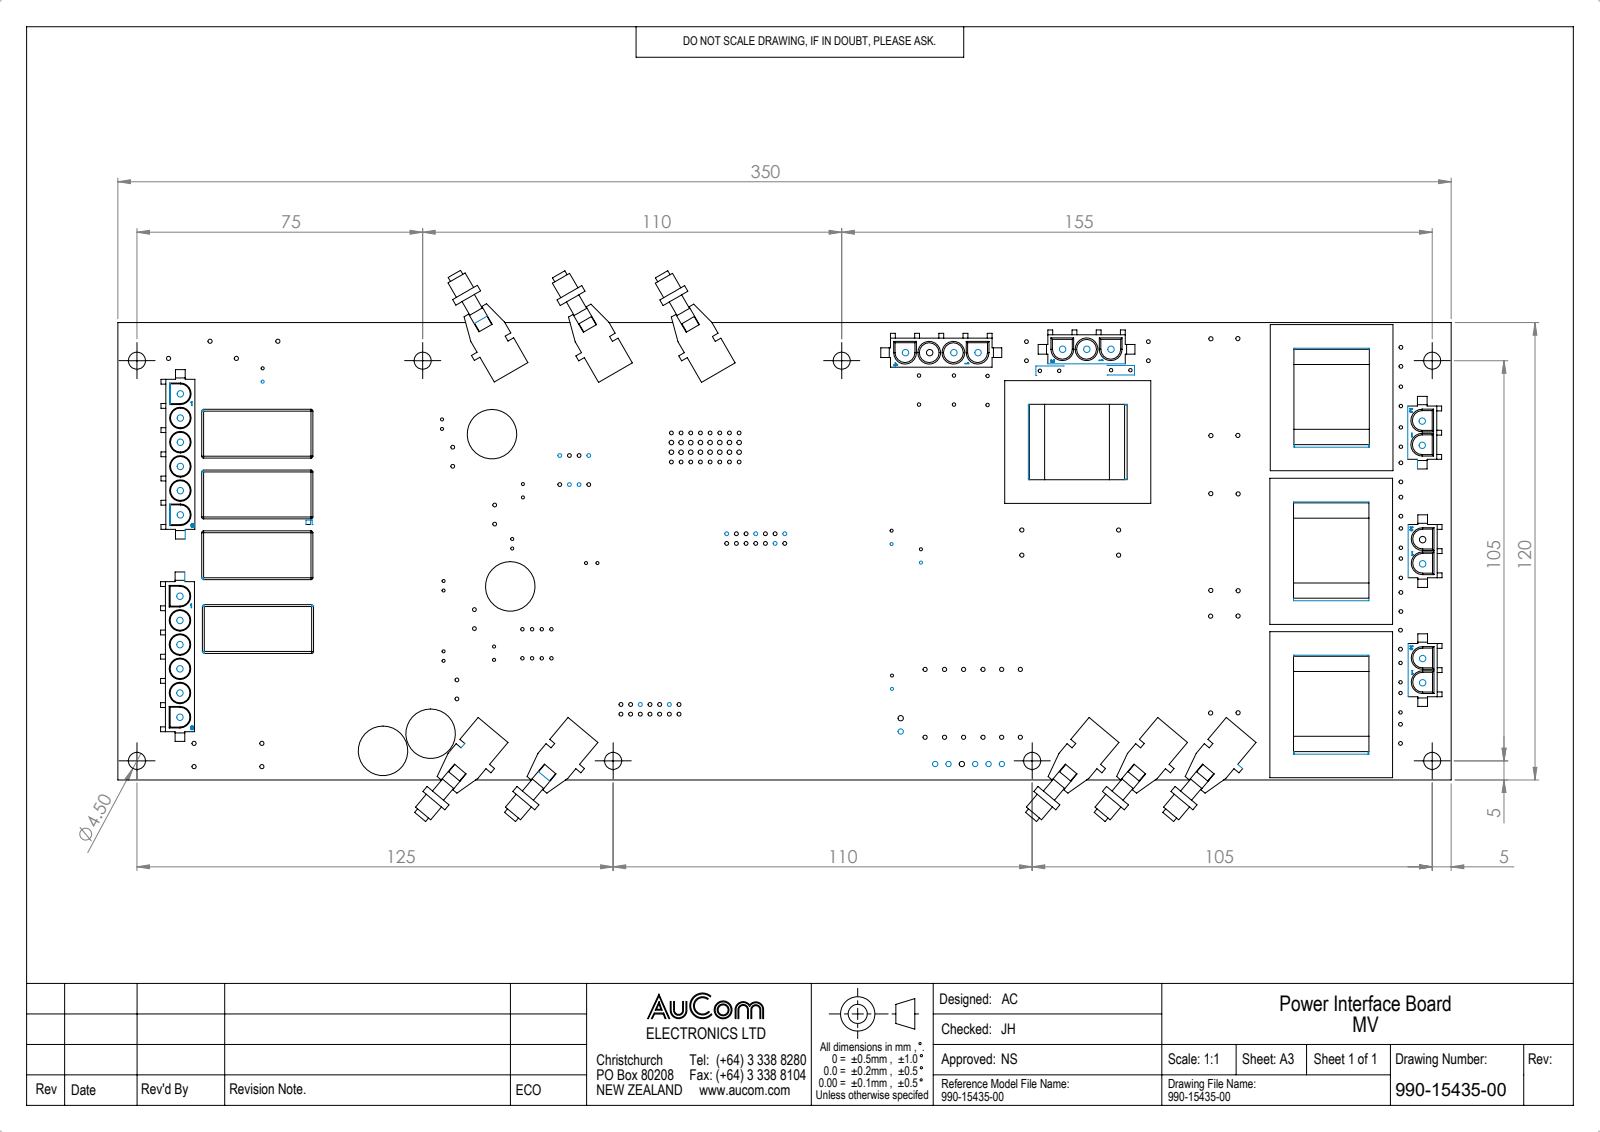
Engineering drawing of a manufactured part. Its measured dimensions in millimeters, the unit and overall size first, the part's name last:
Units: millimetres
Overall size (bounding box): 350 × 144.62 × 30.2
Round holes (diameter × count): ⌀1 ×80, ⌀0.9 ×37, ⌀1.1 ×36, ⌀1.75 ×28, ⌀0.8 ×27, ⌀1.2 ×24, ⌀1.5 ×12, ⌀4.5 ×8, ⌀5.21 ×6, ⌀5.21 ×5, ⌀1.4 ×2, ⌀1.7 ×2
Round bosses / shafts (diameter × count): ⌀0.6 ×48, ⌀7.5 ×8, ⌀5.2 ×8, ⌀4.5 ×8, ⌀3.75 ×8, ⌀13 ×4
Partial cylindrical surfaces — rounded edges, fillets, slot ends (radius × count): R0.3 ×56, R0.5 ×28, R2.6 ×8, R4 ×8, R2.6 ×7, R2.6 ×7
Main face-to-face distances: 1.66, 20.66, 19, 12.8, 15.95, 26, 32.2, 7.62, 38.34, 31.9
Hole centre spacings: 5.08, 5, 25.9, 10.16, 25.4, 27.36, 35.7, 5.32
Bodies: 0 solids, 1801 faces (871 planar, 884 cylindrical, 46 other)
Part name (STEP PRODUCT): 990-15435-00
STEP written by: SolidWorks 2014 (AUTOMOTIVE_DESIGN)
